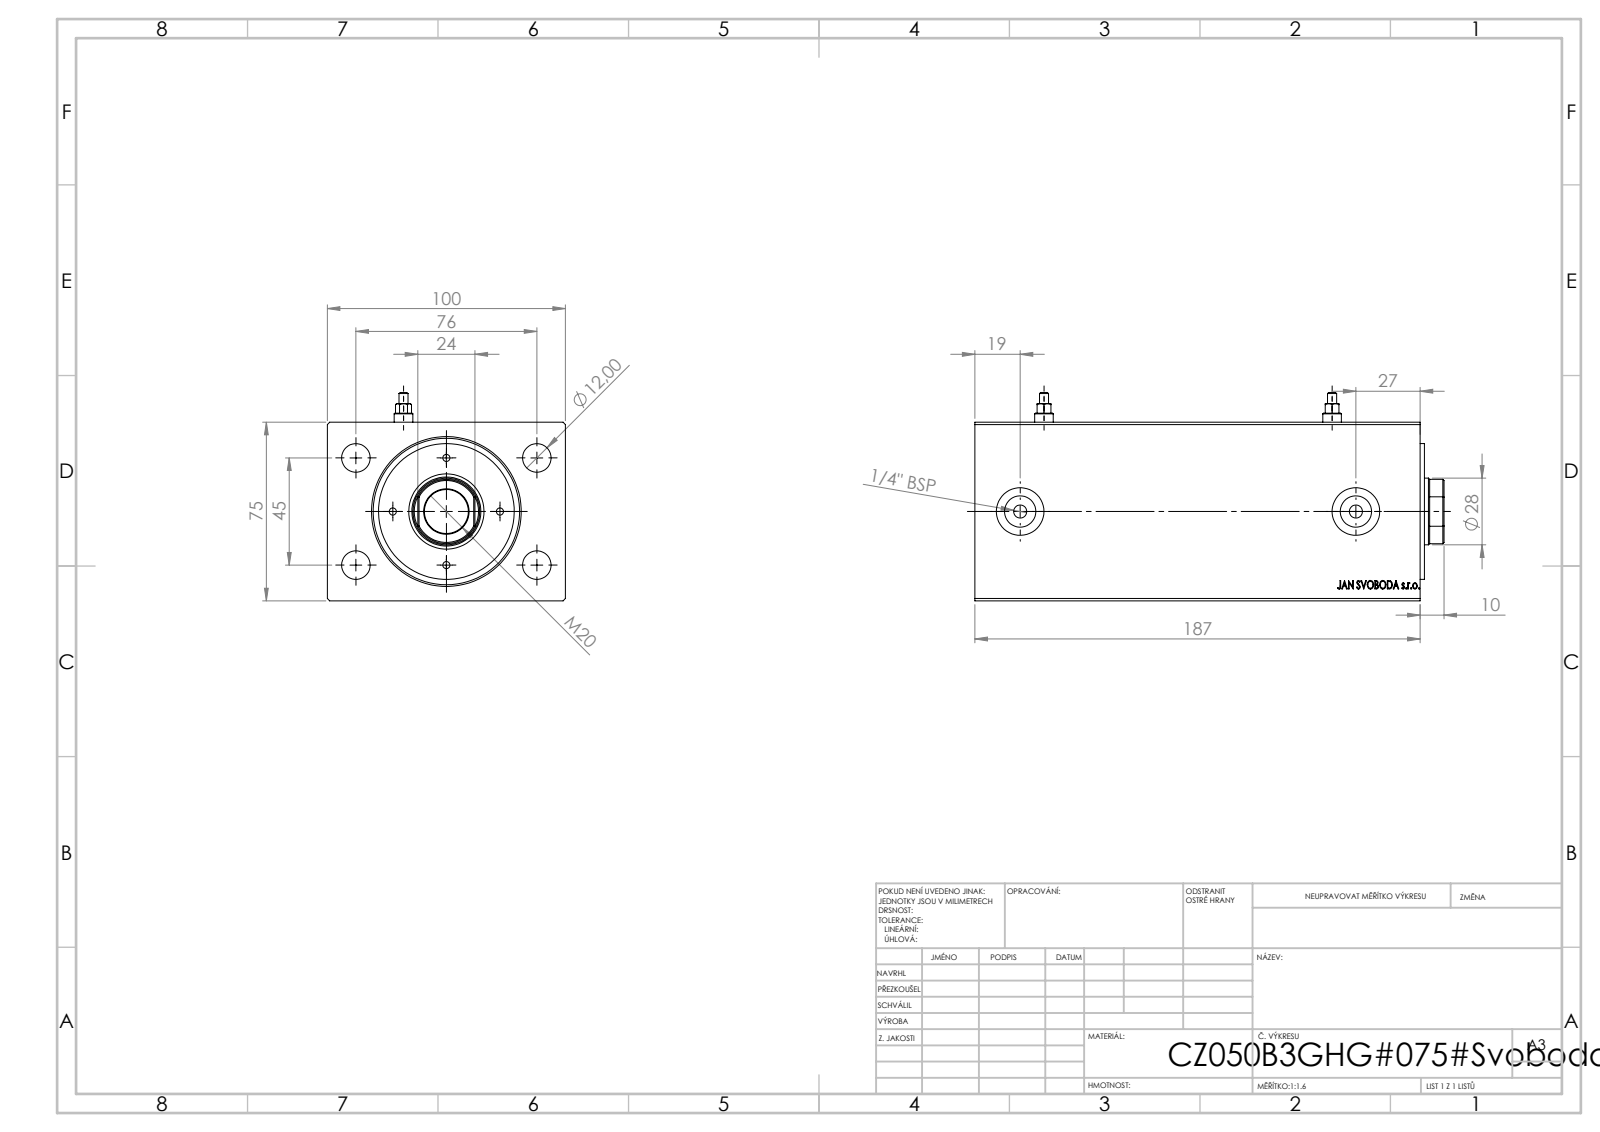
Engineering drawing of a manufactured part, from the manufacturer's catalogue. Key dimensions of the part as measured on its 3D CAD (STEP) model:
Part name (STEP PRODUCT): Zatka_Cushioning3; V500CZ_B_VC; V500CZ
STEP written by: SolidWorks 2019 (CONFIG_CONTROL_DESIGN)
Units: millimetres
Bodies: 5 solids, 934 faces (424 planar, 74 cylindrical, 436 other)
Overall size (bounding box): 197 × 100 × 87.5
Volume: 1 270 000 mm³ · Surface area: 151 255 mm²
Round holes (diameter × count): ⌀3 ×4, ⌀12 ×4, ⌀1.8 ×2, ⌀5.5 ×2, ⌀8 ×2, ⌀13.16 ×2, ⌀20 ×2, ⌀18.5 ×1, ⌀28 ×1, ⌀29 ×1, ⌀36 ×1, ⌀50 ×1
Round bosses / shafts (diameter × count): ⌀7.8 ×2, ⌀3.8 ×2, ⌀57 ×1
Partial cylindrical surfaces — rounded edges, fillets, slot ends (radius × count): R13.5 ×1
Main face-to-face distances: 75, 100, 187, 169.2, 17.8, 10, 1.8, 8.2, 161, 178.8
Hole centre spacings: 22.5, 27.32, 31.82, 38, 44.16, 45, 58.9, 64.55
